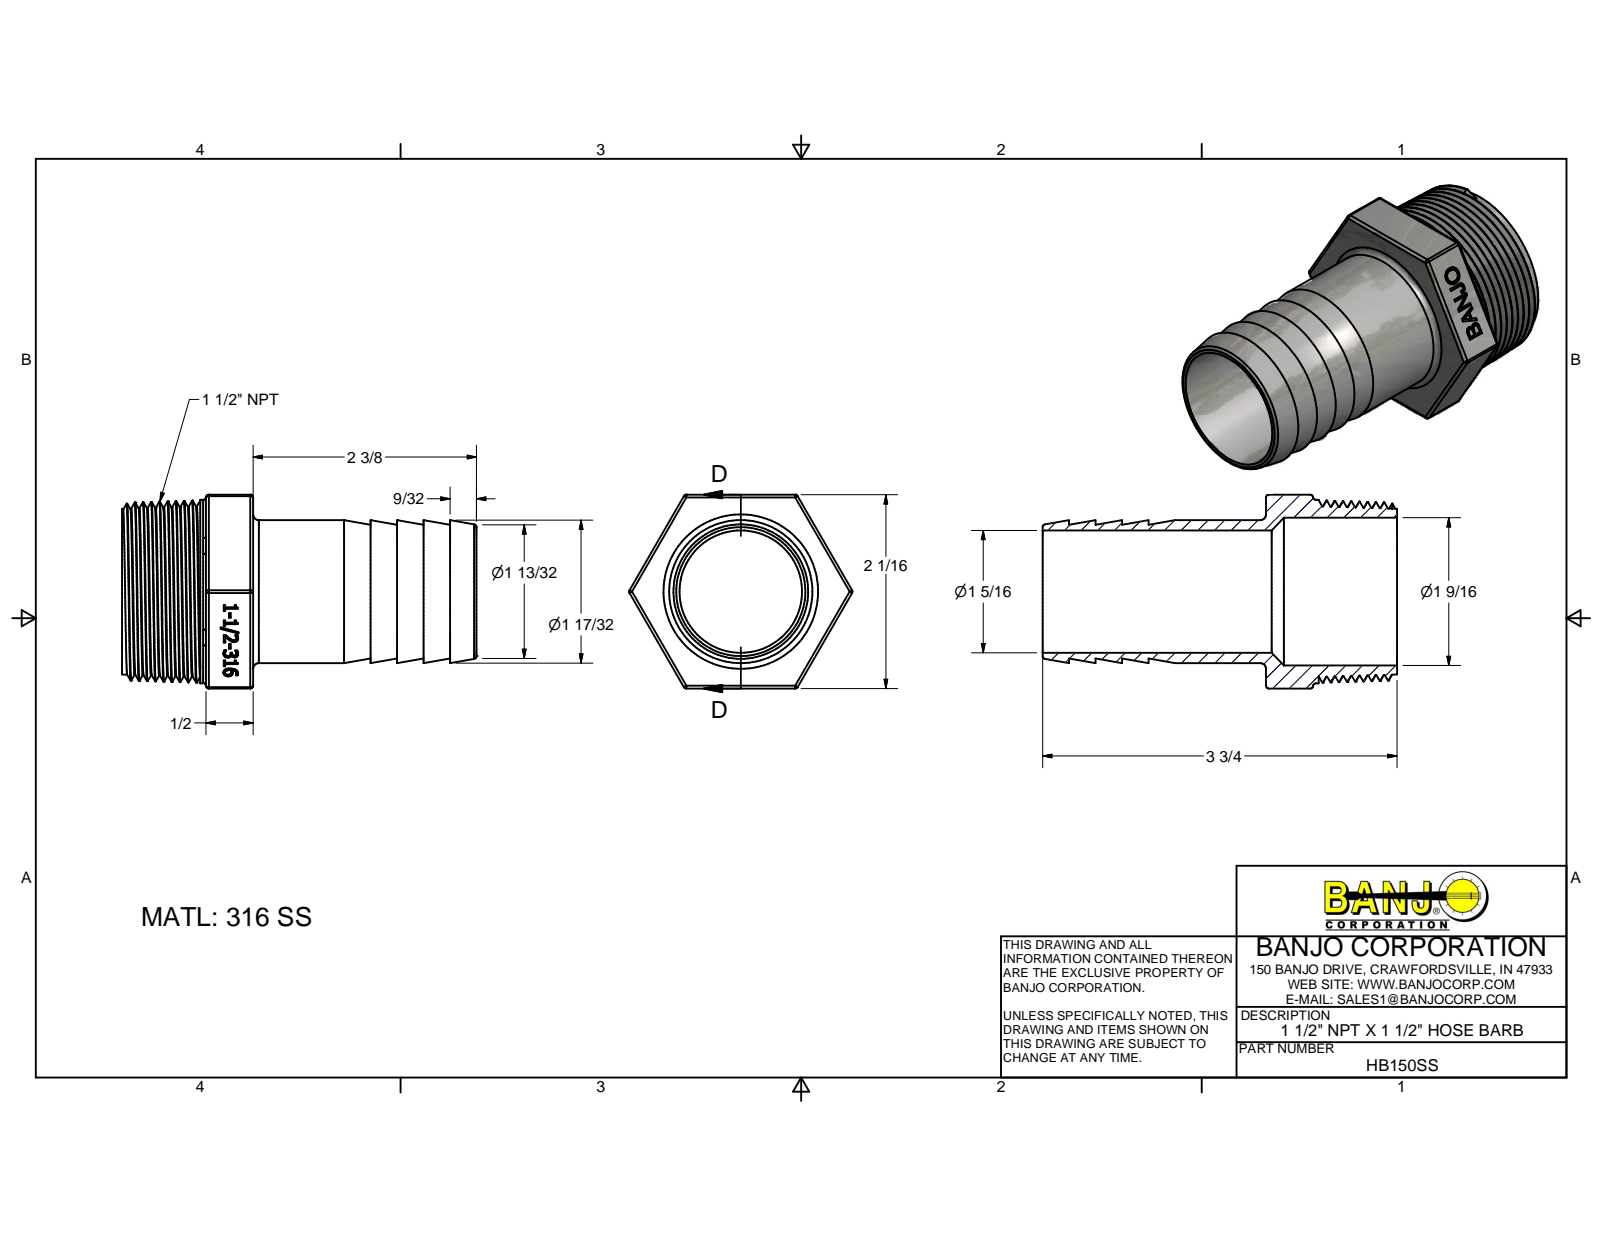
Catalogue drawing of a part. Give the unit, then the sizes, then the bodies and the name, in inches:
Units: inches
Overall size (bounding box): 3.76 × 2.369 × 2.06
Round holes (diameter × count): ⌀1.3 ×1, ⌀1.57 ×1
Round bosses / shafts (diameter × count): ⌀1.95 ×1, ⌀1.52 ×1
Partial cylindrical surfaces — rounded edges, fillets, slot ends (radius × count): R0.03 ×18
Main face-to-face distances: 2.06, 0.281, 1.39, 0.562, 0.843, 0.5, 0.89, 0.281, 2.089, 2.589
Volume: 2.61 in³ · Surface area: 44.62 in²
Bodies: 1 solid, 285 faces (134 planar, 22 cylindrical, 129 other)
Part name (STEP PRODUCT): HB150SS
STEP written by: Autodesk Inventor 2013 (AUTOMOTIVE_DESIGN)
